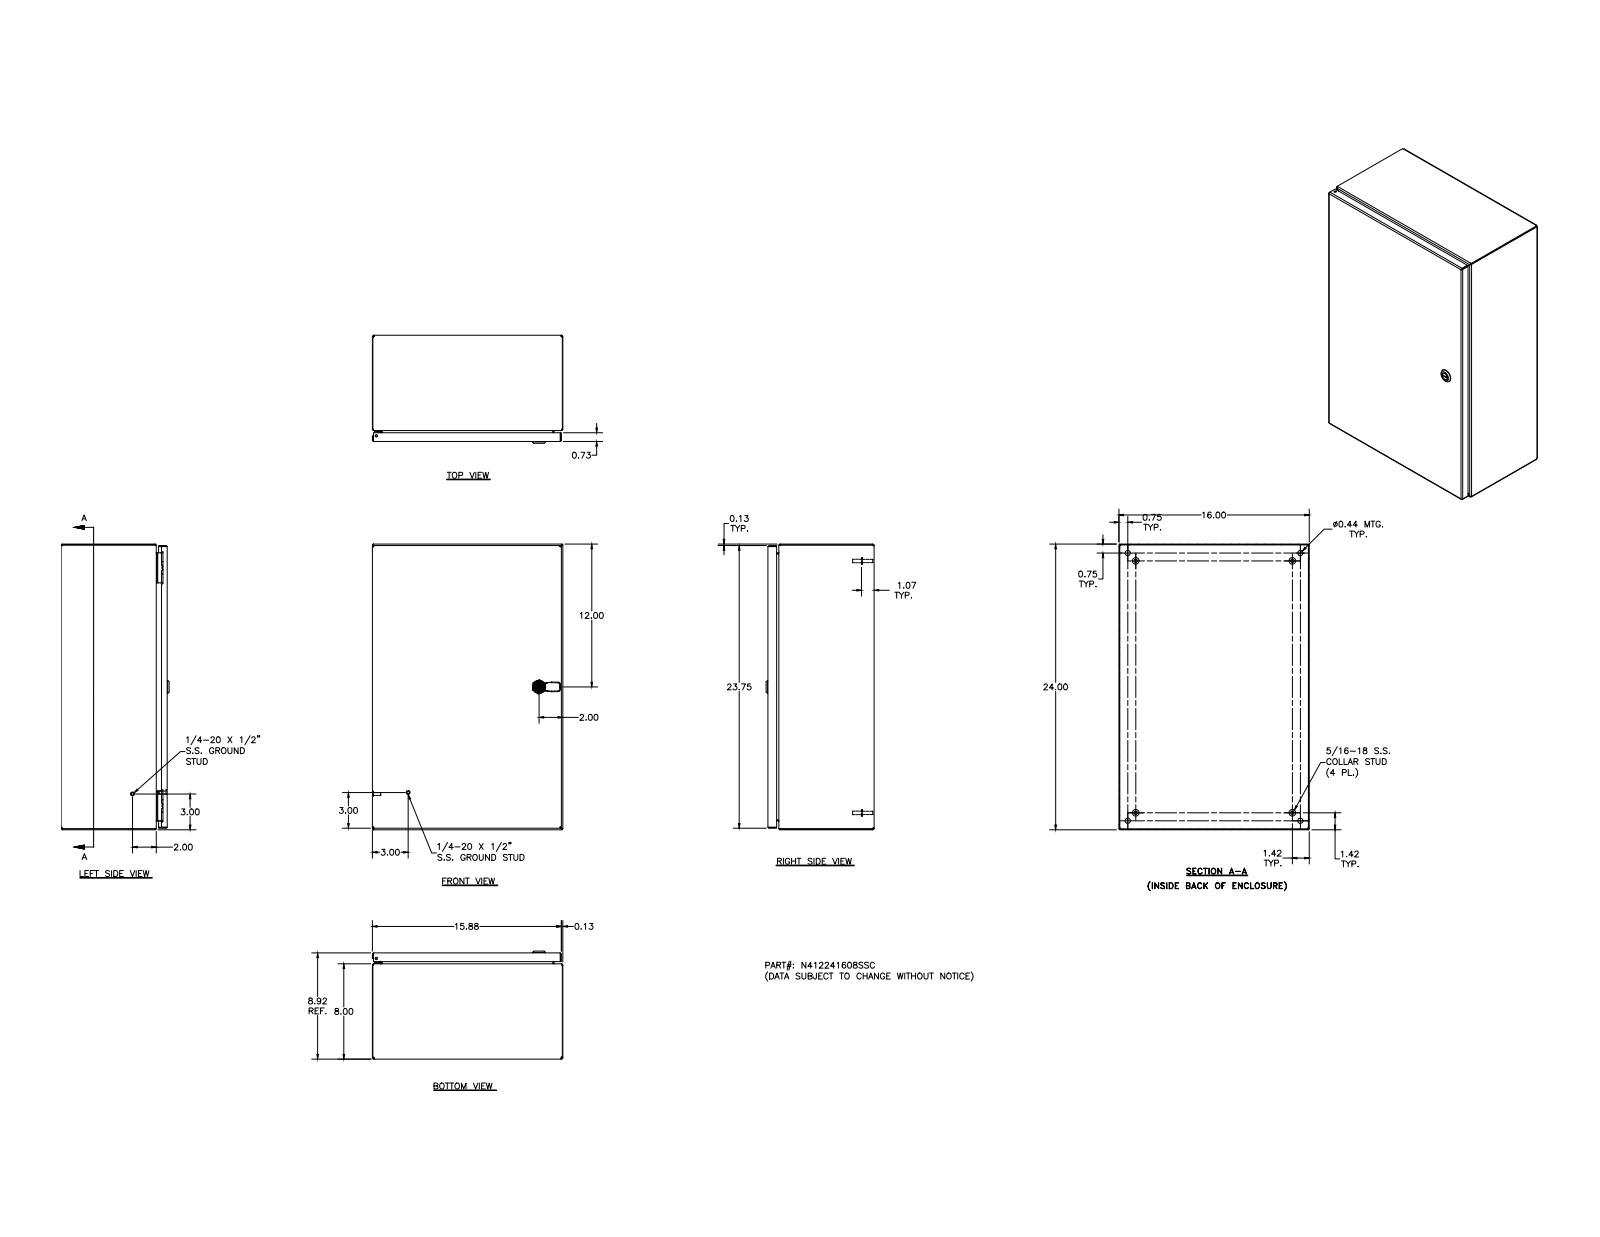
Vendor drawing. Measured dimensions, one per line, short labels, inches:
name: N412241608SSC; N412241608SSCBKP; 388151; N4122416SSCLID (+8 more)
written by: Autodesk Inventor 2011 (AUTOMOTIVE_DESIGN)
unit: in
bodies: 34 solids, 1384 faces (531 planar, 509 cylindrical, 344 other)
size: 24 × 16 × 9.075
volume: 116.2 in³; area: 3 160 in²
holes: 5× ⌀0.188, 4× ⌀0.093, 4× ⌀0.152, 4× ⌀0.167, 4× ⌀0.172, 4× ⌀0.437, 2× ⌀0.156, 1× ⌀0.187, 1× ⌀0.197, 1× ⌀0.315, 1× ⌀0.394, 1× ⌀0.402
bosses: 10× ⌀0.25, 4× ⌀0.563, 4× ⌀0.36, 4× ⌀0.32, 4× ⌀0.3, 4× ⌀0.275, 4× ⌀0.256, 4× ⌀0.164
rounds: 30× R0.031, 26× R0.05, 20× R0.105, 18× R0.016, 14× R0.125, 9× R0.02, 8× R0.032, 8× R0.07
face distances: 0.074, 8.843, 15.926, 8.769, 8.917, 23.926, 16, 15.852, 24, 23.852
hole spacings: 20, 0.017, 0.66, 0.019, 0.5, 0.648, 0.652, 0.656
